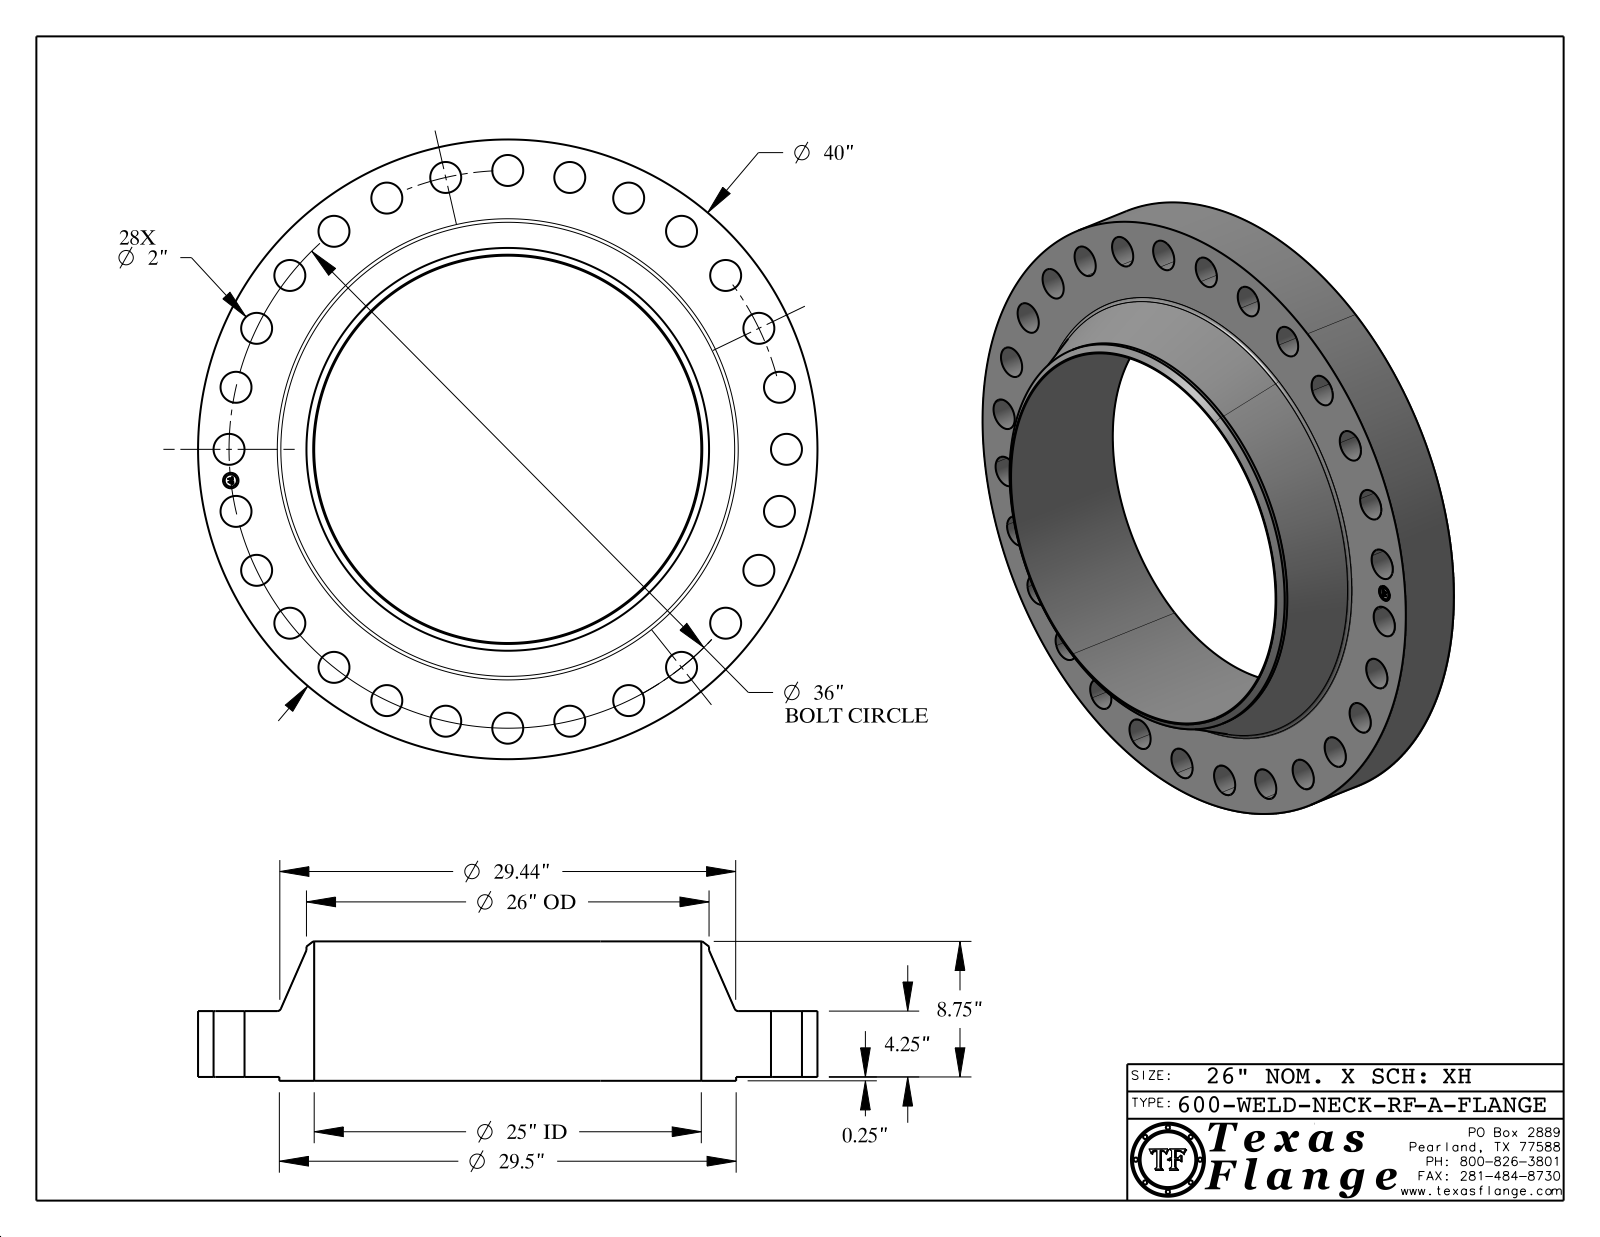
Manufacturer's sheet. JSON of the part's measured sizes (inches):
{"part_name": "600-WELD-NECK-RF, Series A", "step_written_by": "CATIA V5 STEP AP214 (AUTOMOTIVE_DESIGN)", "units": "inches", "bodies": {"solids": 1, "faces": 459, "planar": 369, "cylindrical": 84, "other": 6}, "overall_size": [40, 40, 9], "volume_in3": 3392, "surface_area_in2": 3616, "round_holes": [[2, 28], [1, 1], [25, 1]], "round_bosses_or_shafts": [[0.061, 8], [40, 1], [29.5, 1], [26, 1], [0.788, 1]], "face_to_face_distances": [4.25, 4.5, 0.25, 9, 8.75, 0.015, 4.485, 4.235, 4.515, 0.298], "hole_center_spacings": [18, 19.153, 4.031, 8.011, 11.89, 15.62, 22.446, 25.456]}
